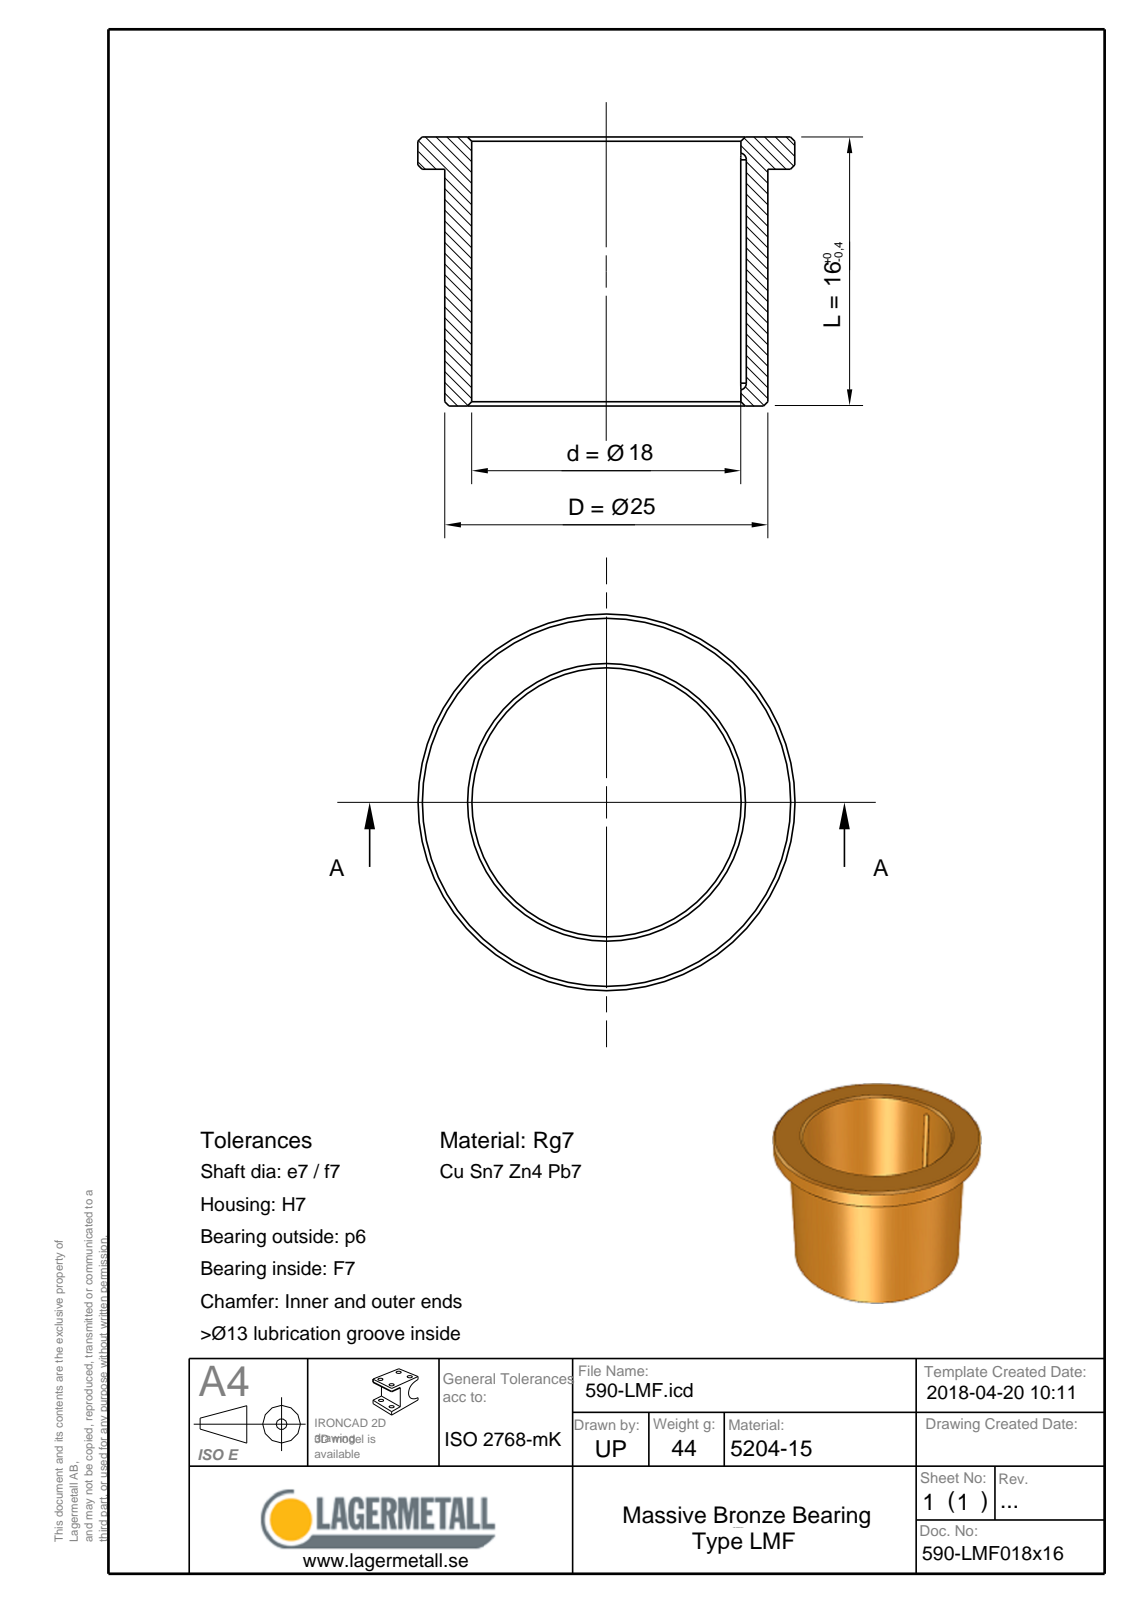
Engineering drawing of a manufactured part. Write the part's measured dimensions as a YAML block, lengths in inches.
part_name: "590-LMF018x16"
step_written_by: "Spatial InterOp 3D (CONFIG_CONTROL_DESIGN)"
units: inches
bodies: {solids: 1, faces: 18, planar: 5, cylindrical: 6, other: 7}
overall_size: [1.26, 1.26, 0.63]
volume: 0.304
surface_area: 5.036
round_holes:
  - {diameter: 0.709, count: 1}
round_bosses_or_shafts:
  - {diameter: 1.26, count: 1}
  - {diameter: 0.984, count: 1}
partial_cylinders:
  - {radius: 0.03, count: 3}
face_to_face_distances: [0.157, 0.472, 0.63, 0.059]
